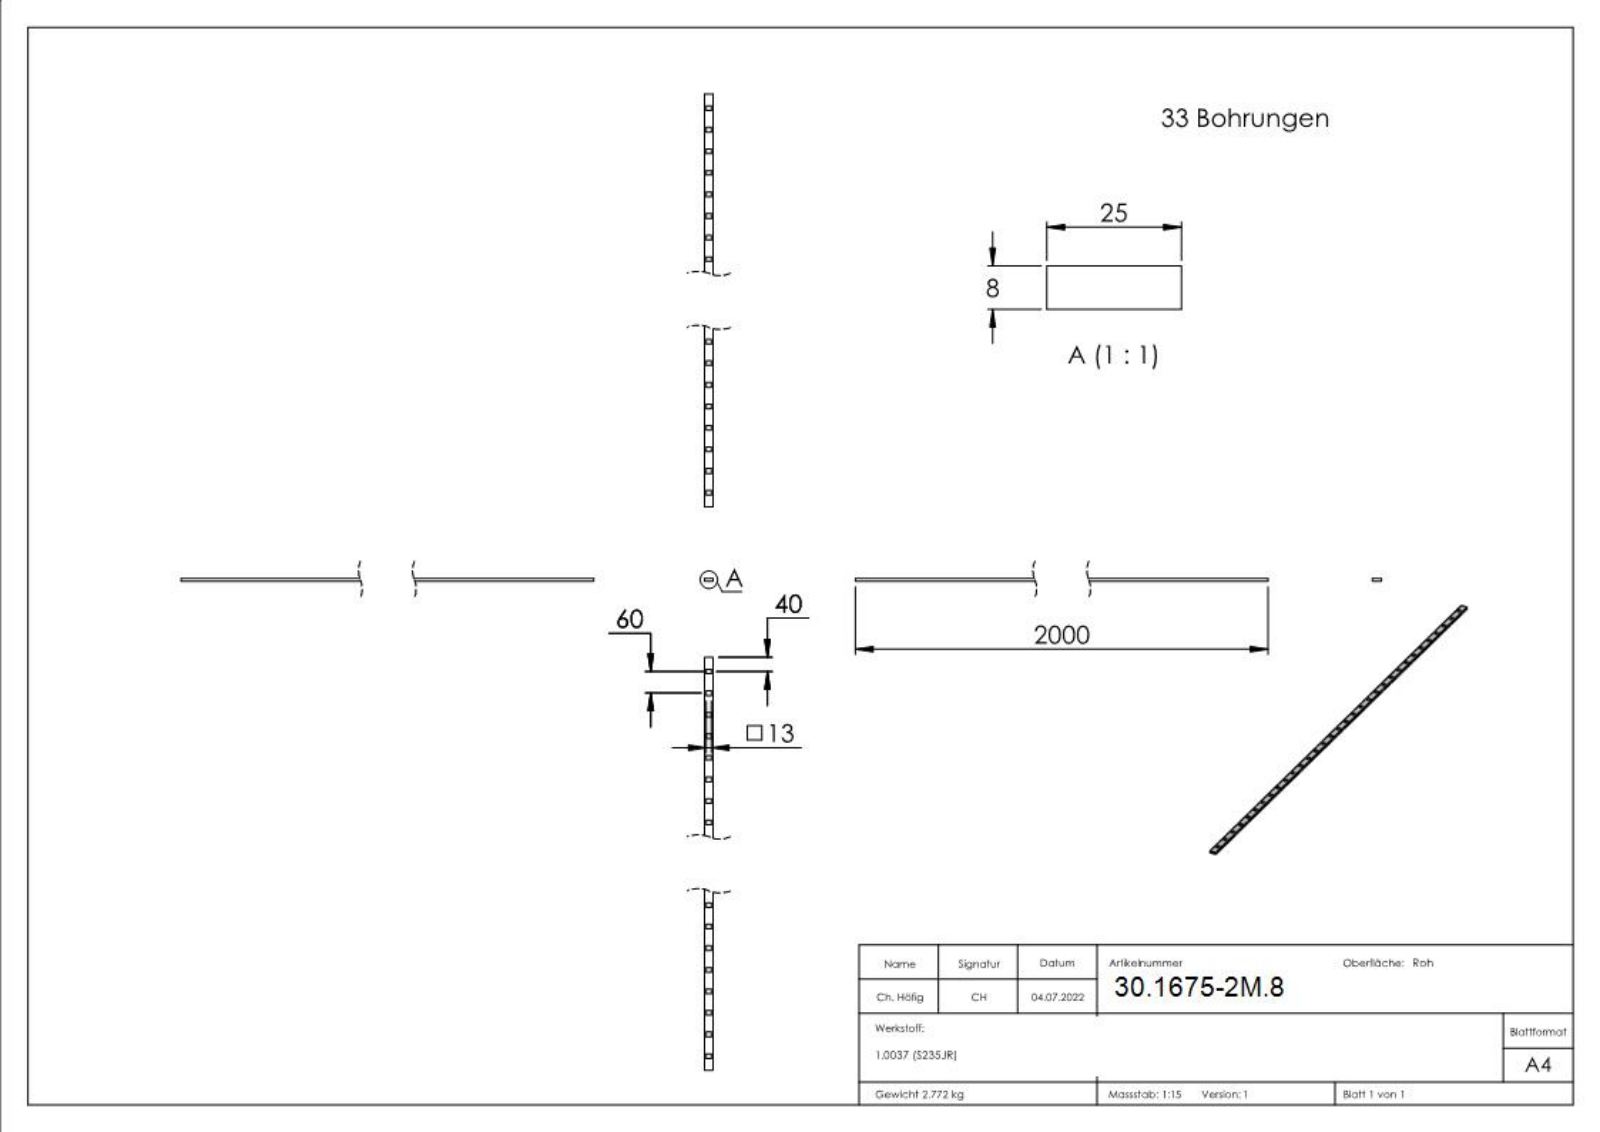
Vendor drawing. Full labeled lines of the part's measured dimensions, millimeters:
Part name (STEP PRODUCT): 1549-8
STEP written by: SolidWorks 2018 (CONFIG_CONTROL_DESIGN)
Units: millimetres
Bodies: 1 solid, 370 faces (268 planar, 0 cylindrical, 102 other)
Overall size (bounding box): 2000 × 25 × 8
Volume: 355 383 mm³ · Surface area: 134 984 mm²
Main face-to-face distances: 8, 25, 6, 19, 13, 60, 120, 180, 240, 300
